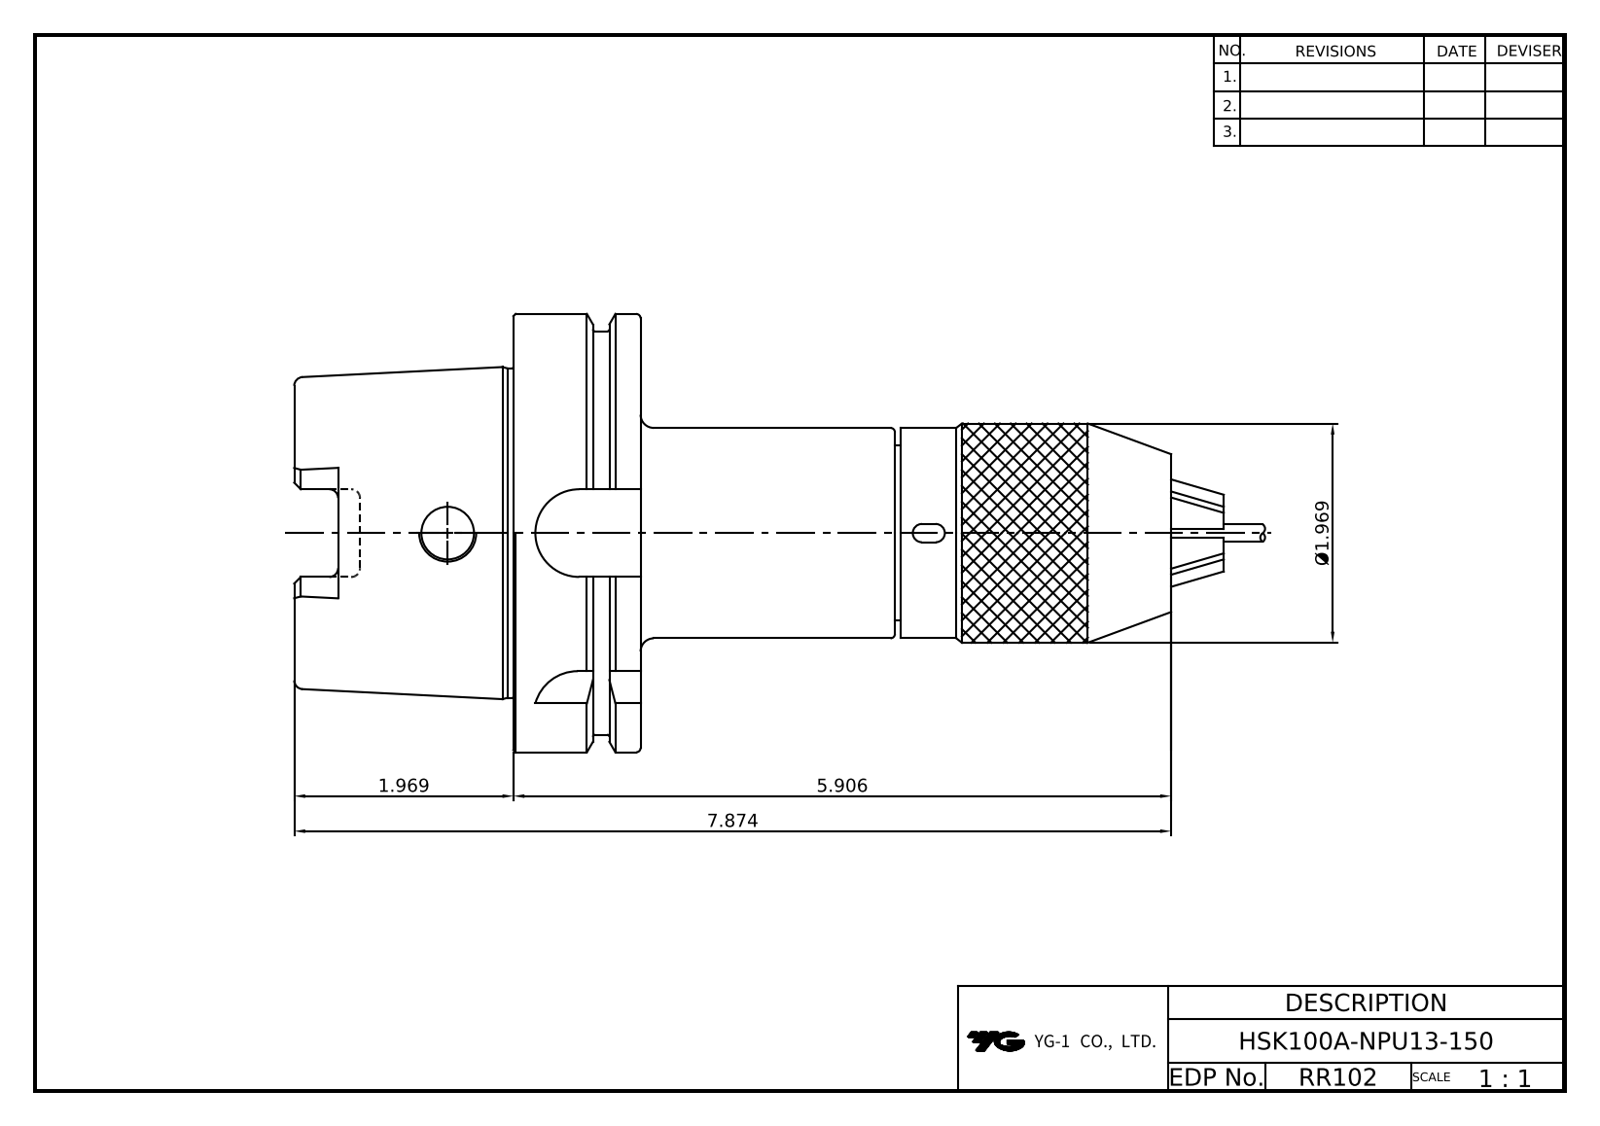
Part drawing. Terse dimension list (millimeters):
name: LO-HSK100A-NPU13-150; NPU13; BB1271306M401A; BB12713070101A (+2 more)
written by: Autodesk Inventor 2024 (AUTOMOTIVE_DESIGN)
unit: mm
bodies: 7 solids, 271 faces (153 planar, 60 cylindrical, 58 other)
size: 211.53 × 100 × 100
volume: 475 082 mm³; area: 86 390 mm²
holes: 1× ⌀9, 1× ⌀10, 1× ⌀12, 1× ⌀14, 1× ⌀22.38, 1× ⌀23.5, 1× ⌀25, 1× ⌀33.5, 1× ⌀44, 1× ⌀53, 1× ⌀63
bosses: 1× ⌀100, 1× ⌀92, 1× ⌀75.41, 1× ⌀50, 1× ⌀49.4, 1× ⌀48, 1× ⌀42, 1× ⌀38
rounds: 6× R0.3, 6× R2, 6× R2.5, 4× R4.88, 4× R10, 3× R1, 3× R9
face distances: 72, 29, 101, 16.5, 12.5, 69.5, 40.5, 31.5, 57, 88.5
